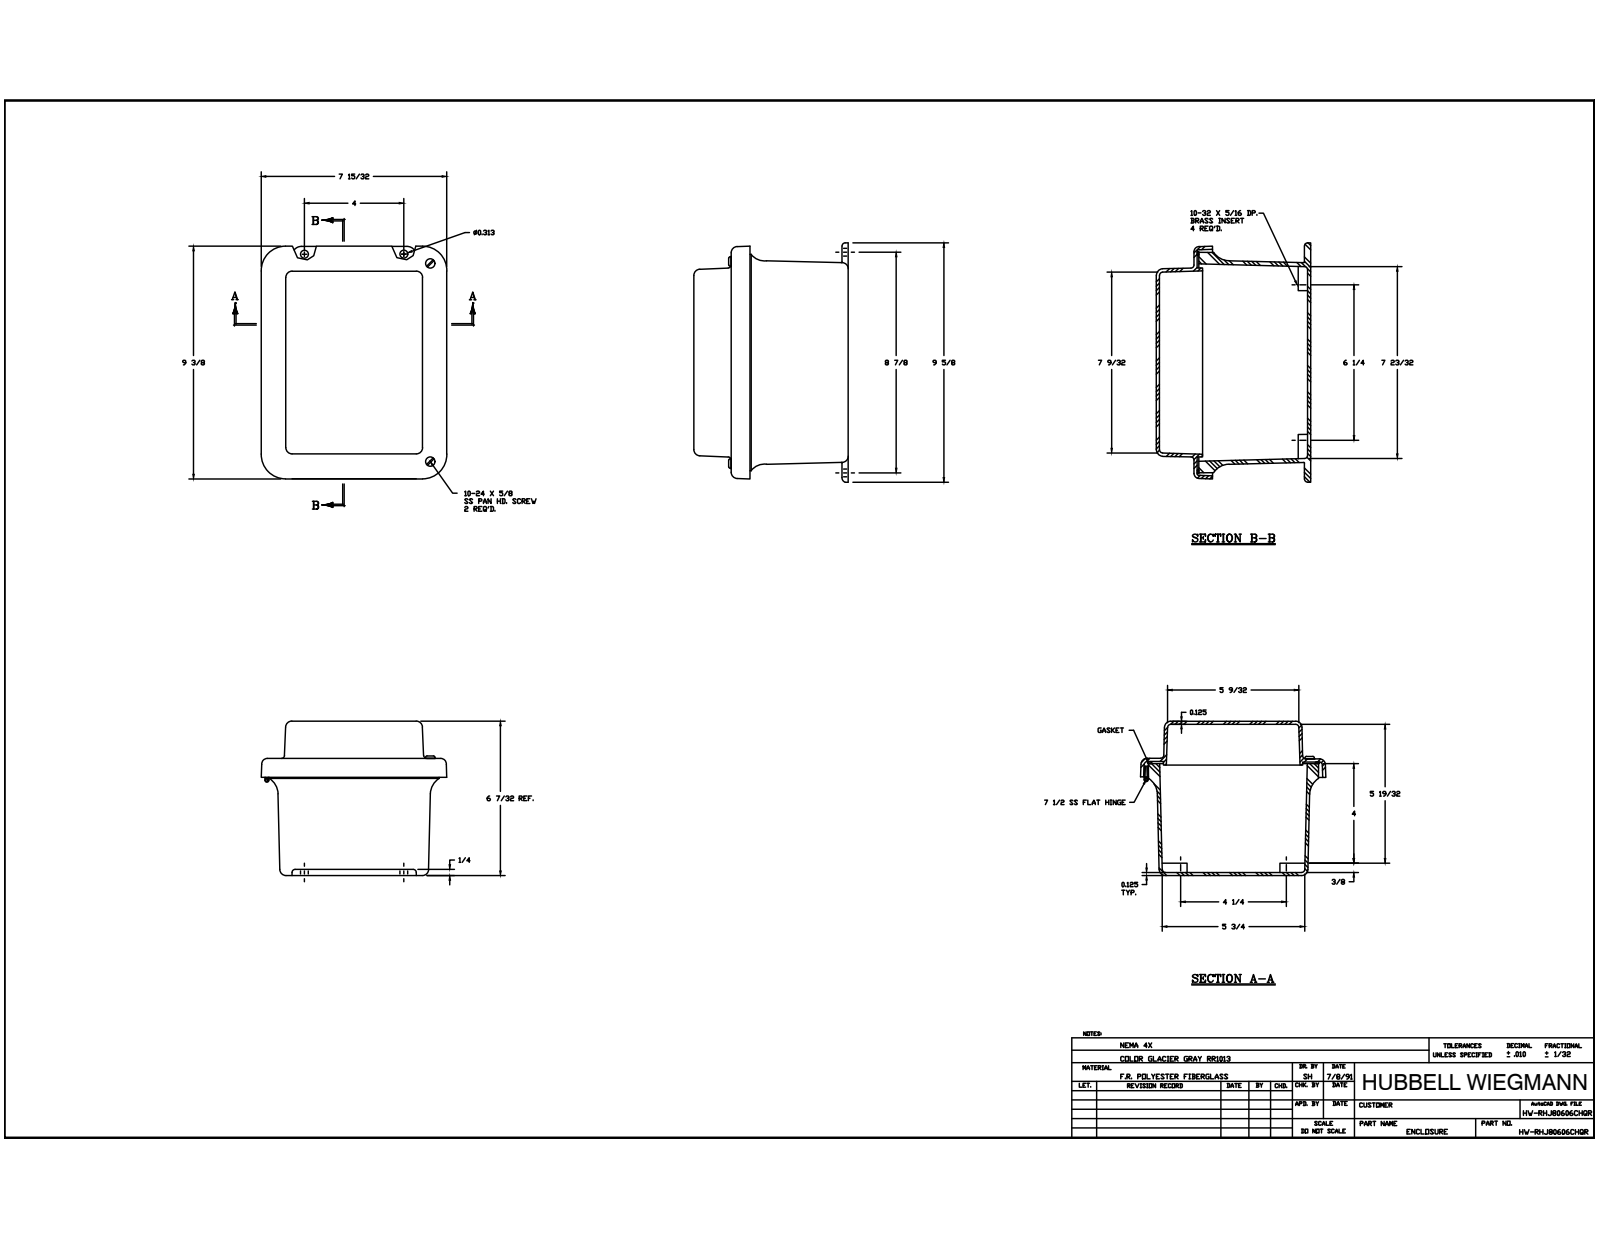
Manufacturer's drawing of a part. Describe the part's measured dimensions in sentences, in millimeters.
The part is named "J806HL_3; RMINS45821P_59; RMINS45821P_60; RMINS45821P_61 (+8 more)". Its 3-D file was written by "Autodesk Inventor 2014 (AUTOMOTIVE_DESIGN)". It is 25 solids with 745 faces: 301 planar, 292 cylindrical and 152 other. Overall it measures 244.47 by 191.85 by 157.85 millimeters. Its volume is 797 789 cubic millimeters and its surface area 444 839 square millimeters. Round holes: 12 of diameter 3.56, 6 of diameter 3.33, 5 of diameter 3.86, 4 of diameter 2.64, 4 of diameter 3.96, 4 of diameter 5.54, 2 of diameter 3.3, 2 of diameter 3.43, 1 of diameter 2.16, 1 of diameter 9.52. Round bosses or shafts: 9 of diameter 3.17, 5 of diameter 6.35, 4 of diameter 6.86, 1 of diameter 7.62, 1 of diameter 4.31, 1 of diameter 3.94, 1 of diameter 3.05. Partial cylindrical surfaces (rounded edges, fillets, slot ends): 24 of radius 3.17, 20 of radius 0.79, 12 of radius 0.38, 12 of radius 6.35, 8 of radius 1.14, 6 of radius 0.76, 5 of radius 0.57, 4 of radius 1.52. The main face-to-face distances are 3.17, 3.18, 38.48, 151.5, 113.02, 154.68, 157.85, 154.67, 116.2, 41.65. The hole center spacings are 88.9, 6.35, 19.06, 23.81, 33.68, 133.89, 184.12, 225.15.
